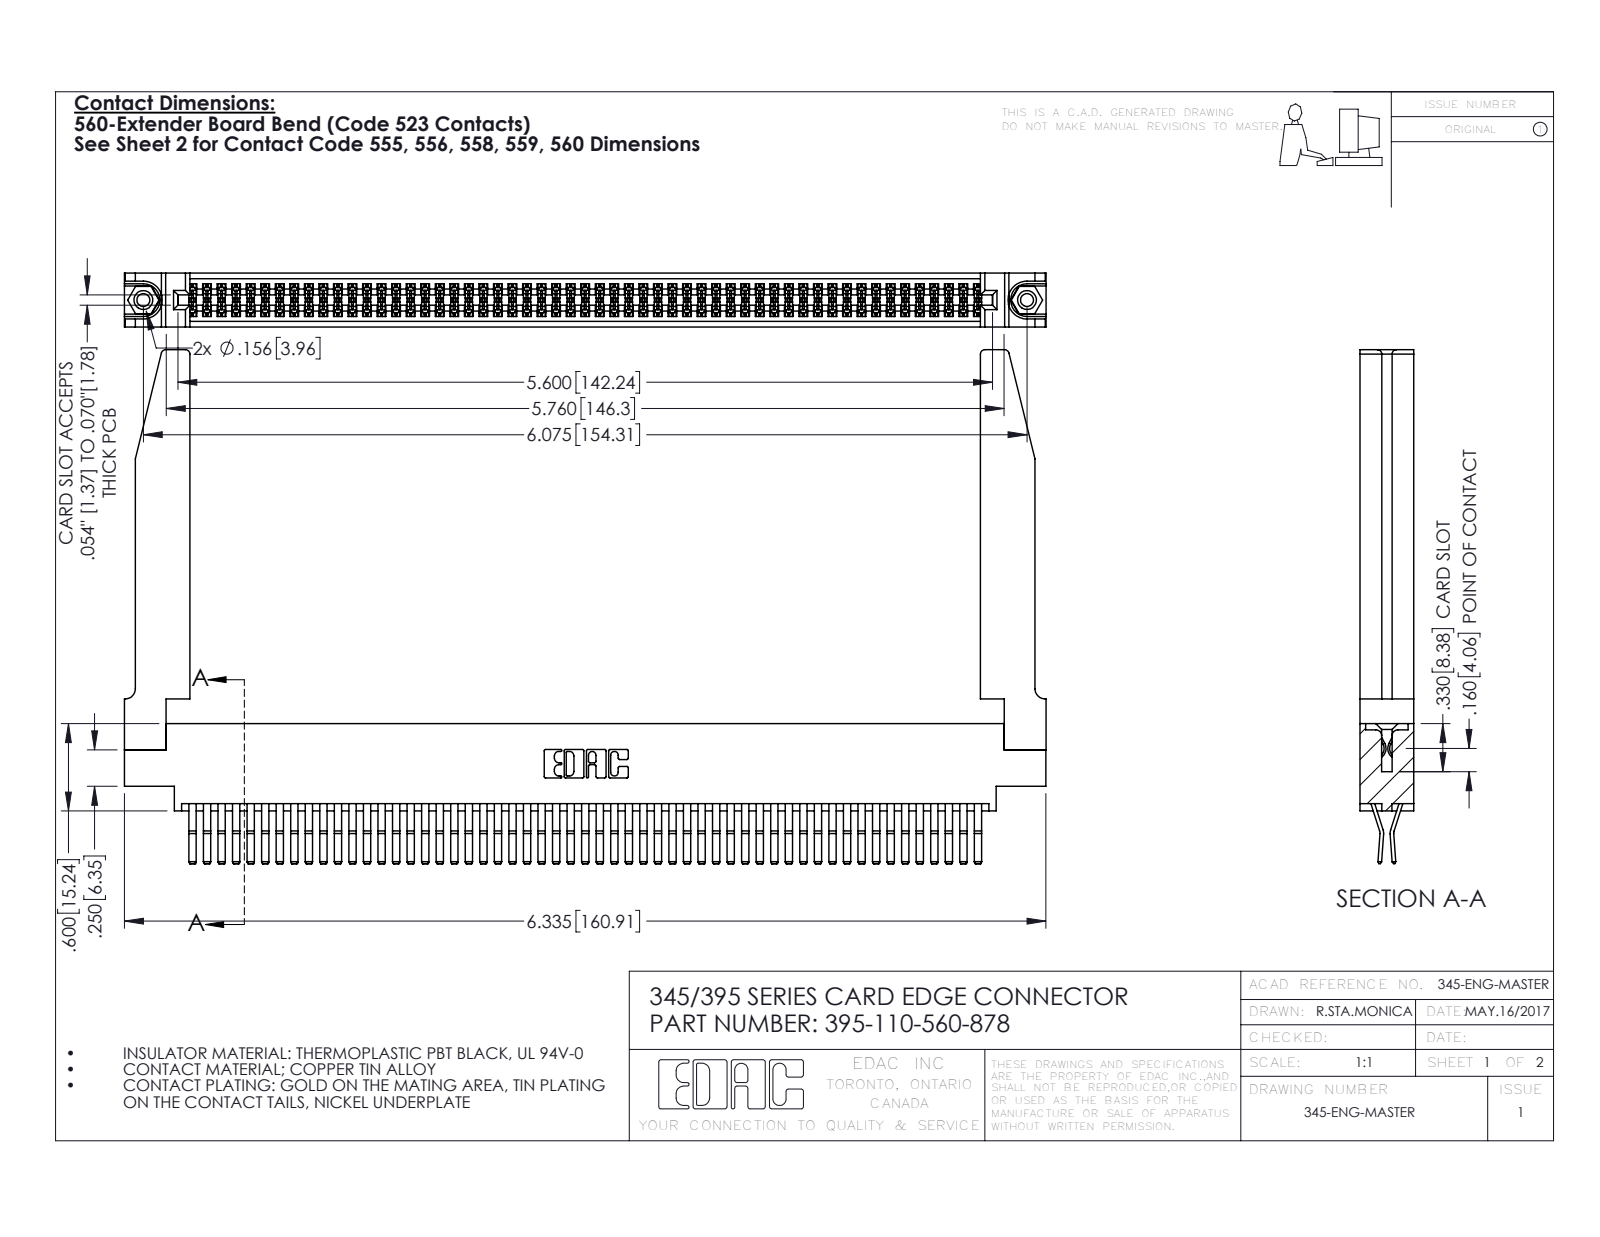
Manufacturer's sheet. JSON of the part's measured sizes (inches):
{"part_name": "345-292-001_560 Tail; 345-220-078_345-220-078; 395-110-560-878; 345-250-001_345-250-001-102 (+1 more)", "step_written_by": "SolidWorks 2016 (CONFIG_CONTROL_DESIGN)", "units": "inches", "bodies": {"solids": 115, "faces": 6084, "planar": 3856, "cylindrical": 2176, "other": 52}, "overall_size": [6.336, 3.532, 0.37], "volume_in3": 1.473, "surface_area_in2": 51.57, "round_holes": [[0.089, 2], [0.125, 2], [0.156, 2], [0.064, 1]], "round_bosses_or_shafts": [[0.155, 2]], "partial_cylinders_radius": [[0.006, 165], [0.01, 22], [0.03, 8], [0.007, 6], [0.031, 6], [0.026, 3], [0.01, 2], [0.014, 2]], "face_to_face_distances": [0.37, 0.072, 0.298, 0.025, 0.098, 0.272, 0.2, 0.225, 0.175, 0.148], "hole_center_spacings": [0.27, 5.839, 6.075]}
